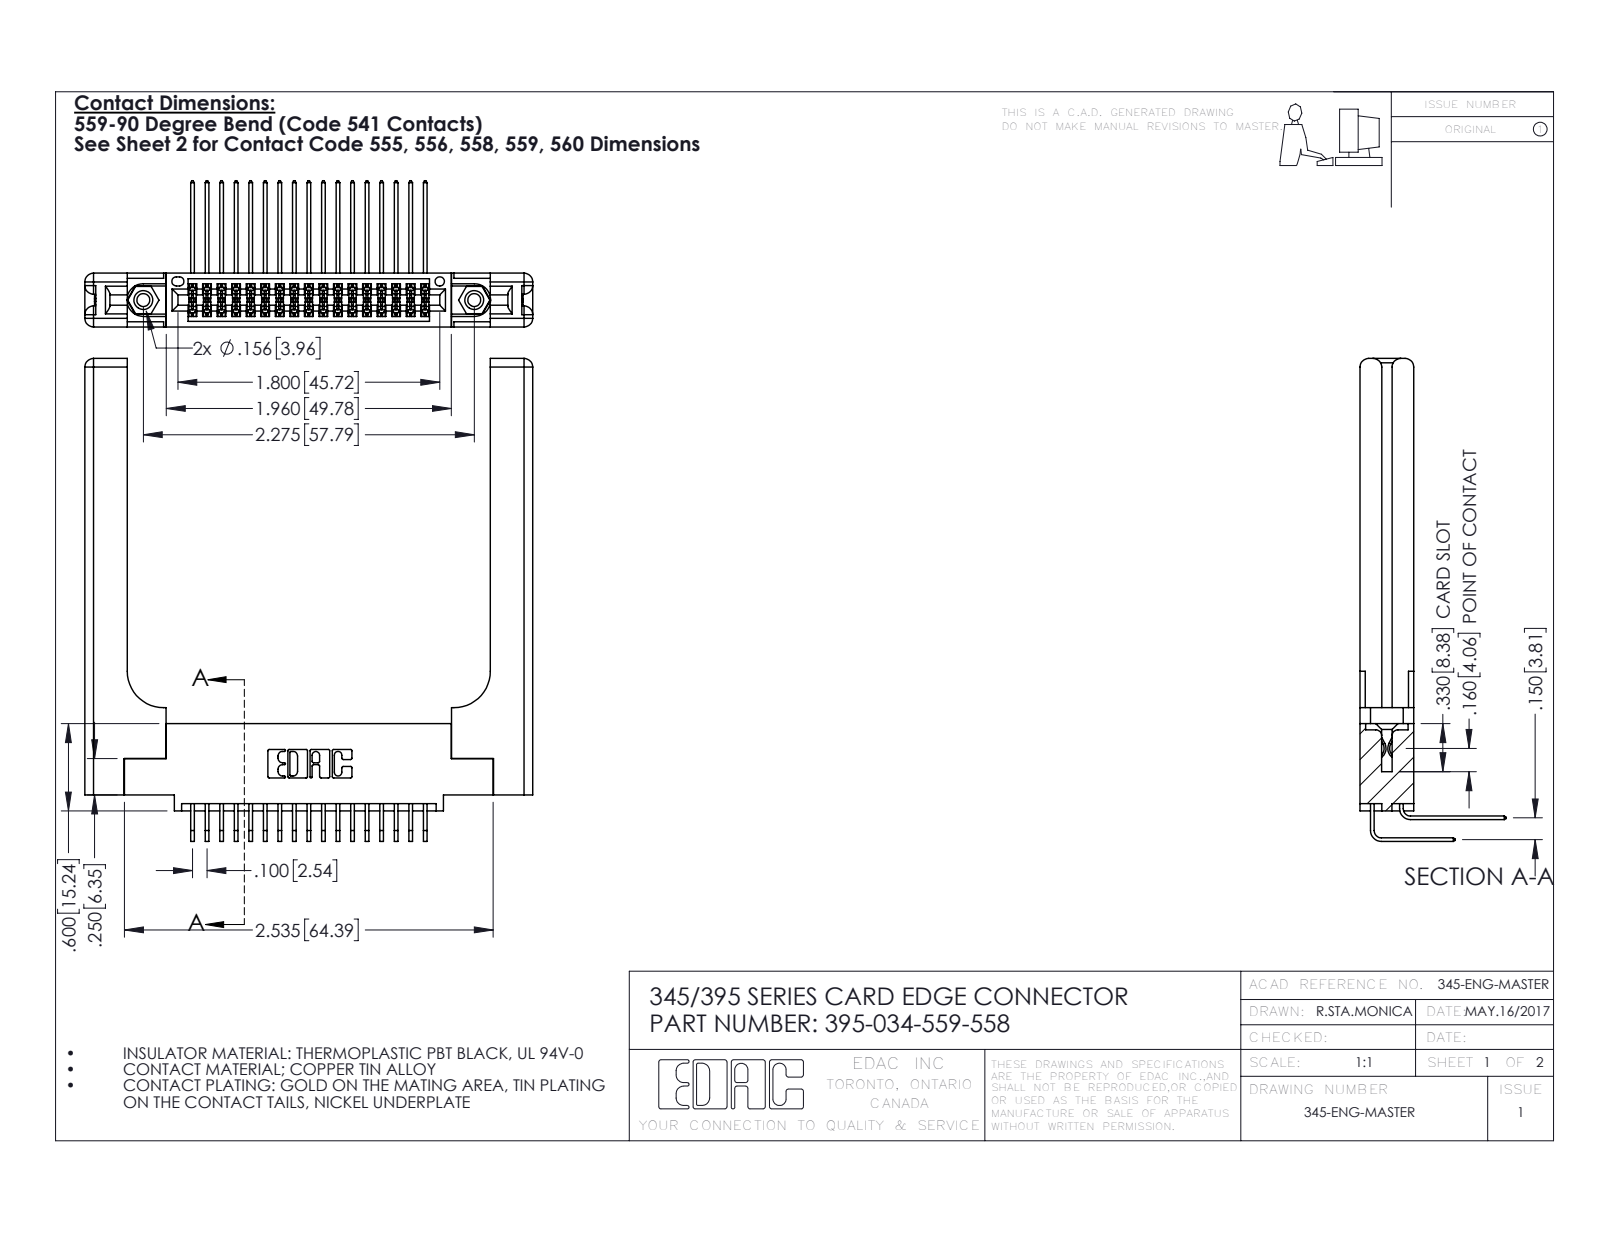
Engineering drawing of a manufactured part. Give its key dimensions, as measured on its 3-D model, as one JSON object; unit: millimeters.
{"part_name": "345-292-001_559 Tail - 2; 345-220-058_345-220-058; 345 Part_0.110 Offset - 0.156 Dia-TH; 345-250-001_345-250-001-102 (+2 more)", "step_written_by": "SolidWorks 2016 (CONFIG_CONTROL_DESIGN)", "units": "millimeters", "bodies": {"solids": 39, "faces": 2154, "planar": 1422, "cylindrical": 672, "other": 60}, "overall_size": [84.3, 78.2, 25.5], "volume_mm3": 16000, "surface_area_mm2": 16660, "round_holes": [[2.3, 2], [3.2, 2], [4, 2], [1.6, 1]], "round_bosses_or_shafts": [[3.9, 2]], "partial_cylinders_radius": [[0.2, 52], [0.3, 22], [1.5, 16], [0.2, 6], [0.8, 6], [0.7, 3], [0.4, 2], [0.5, 2]], "face_to_face_distances": [9.4, 1.8, 7.6, 3.8, 3.8, 2, 5.6, 5.7, 2.5, 6.9], "hole_center_spacings": [6.9, 51.8, 57.8]}
